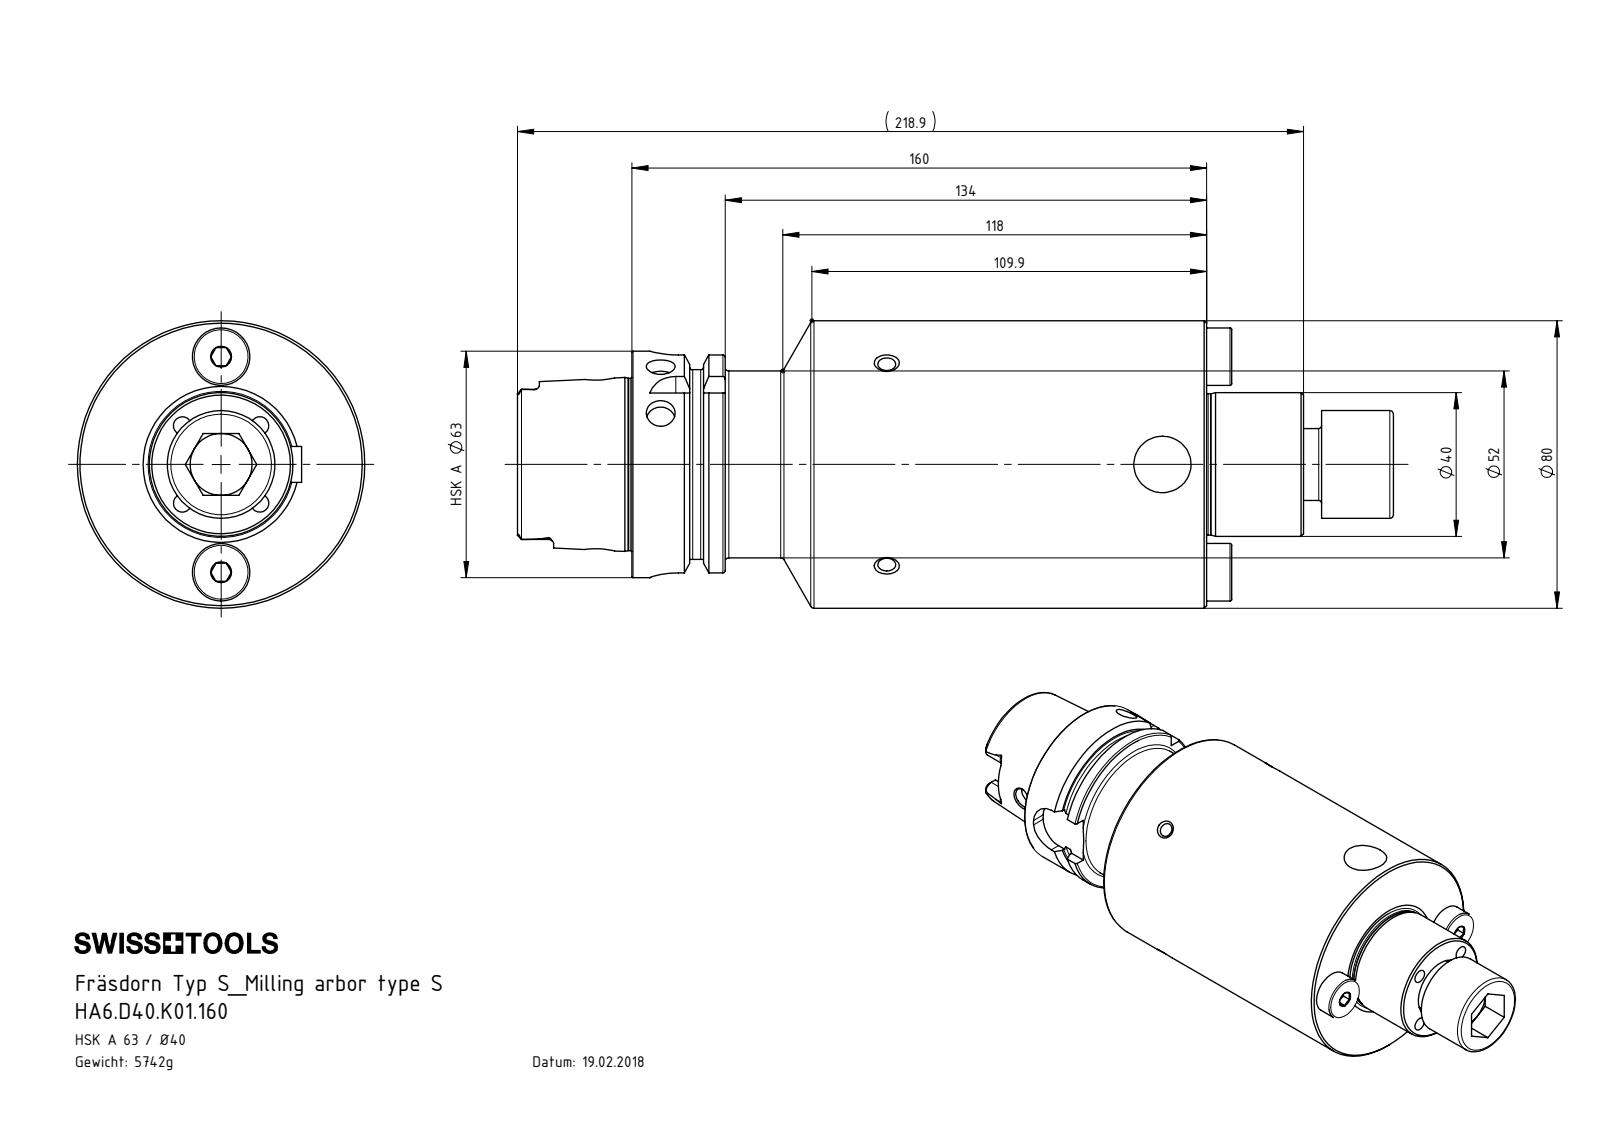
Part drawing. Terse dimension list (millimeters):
name: HA6.D40.K01.160; D40-ER1.002.040_A; D40-ER2.001.023_B; HA6-D40.K01.160_D_Fertigbearbeitung (+1 more)
written by: SolidWorks 2017 (AUTOMOTIVE_DESIGN)
unit: mm
bodies: 5 solids, 393 faces (96 planar, 120 cylindrical, 177 other)
size: 243.9 × 80 × 80
volume: 731 513 mm³; area: 82 699 mm²
holes: 12× ⌀5, 2× ⌀8, 2× ⌀14, 1× ⌀7.5, 1× ⌀8.4, 1× ⌀10, 1× ⌀17, 1× ⌀17.5, 1× ⌀19, 1× ⌀21, 1× ⌀34, 1× ⌀40
bosses: 2× ⌀16, 2× ⌀6, 2× ⌀4.6, 1× ⌀80, 1× ⌀63, 1× ⌀54.95, 1× ⌀52, 1× ⌀47.94
rounds: 6× R1.4, 4× R2.88, 4× R5, 4× R8
face distances: 160, 25, 187, 27, 20, 134.05, 16, 25.95, 161.05, 7
hole spacings: 15.25, 21.56, 22.04, 42.18, 78.05, 30, 30.49, 60
